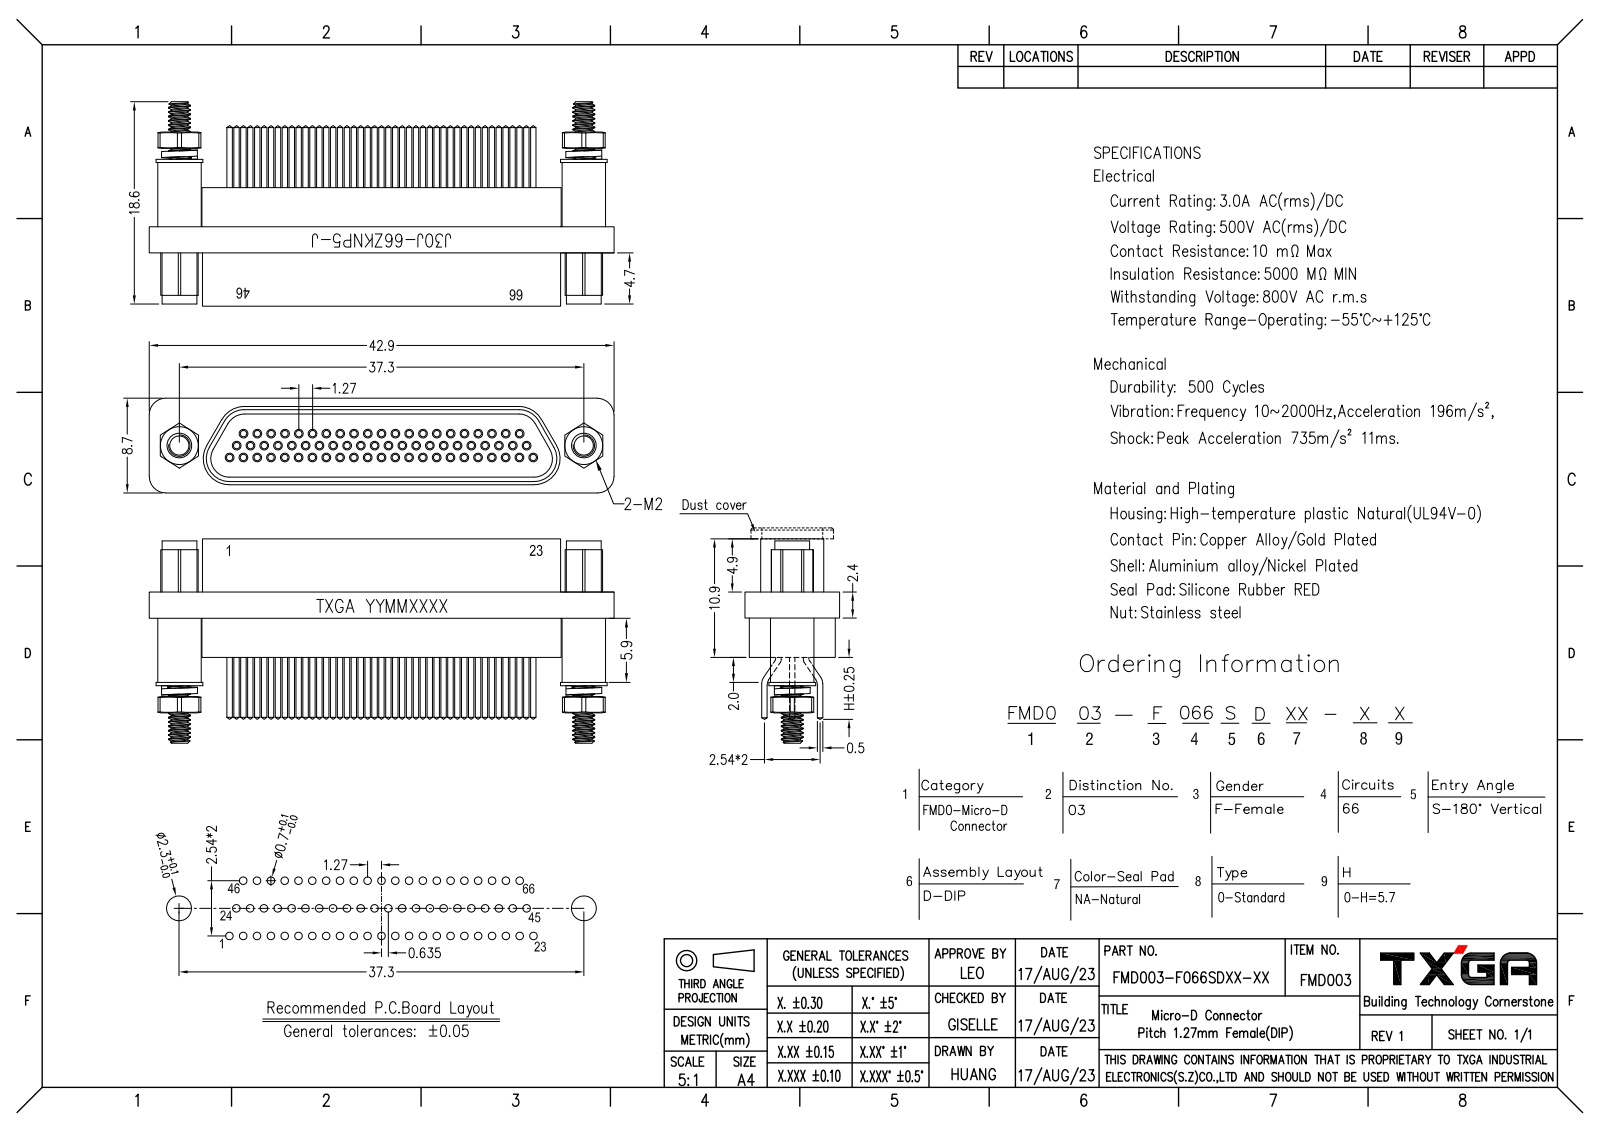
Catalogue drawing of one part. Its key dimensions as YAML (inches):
part_name: "FMD003-F066SDNA-00"
step_written_by: "SolidWorks 2021 (CONFIG_CONTROL_DESIGN)"
units: inches
bodies: {solids: 1, faces: 2411, planar: 753, cylindrical: 838, other: 820}
overall_size: [1.689, 0.74, 0.343]
volume: 0.149
surface_area: 6.891
round_holes:
  - {diameter: 0.024, count: 66}
  - {diameter: 0.063, count: 2}
  - {diameter: 0.083, count: 2}
  - {diameter: 0.087, count: 2}
  - {diameter: 0.091, count: 2}
  - {diameter: 0.126, count: 2}
round_bosses_or_shafts:
  - {diameter: 0.02, count: 154}
  - {diameter: 0.031, count: 66}
  - {diameter: 0.169, count: 2}
  - {diameter: 0.157, count: 2}
  - {diameter: 0.138, count: 2}
  - {diameter: 0.122, count: 2}
  - {diameter: 0.079, count: 2}
partial_cylinders:
  - {radius: 0.012, count: 12}
  - {radius: 0.059, count: 4}
  - {radius: 0.067, count: 4}
  - {radius: 0.079, count: 4}
  - {radius: 0.094, count: 4}
face_to_face_distances: [0.028, 0.236, 0.256, 0.014, 0.041, 0.27, 0.297, 0.327, 0.03, 0.016]
hole_center_spacings: [0.05, 0.1, 0.15, 0.2, 0.25, 0.3, 0.35, 0.4]
